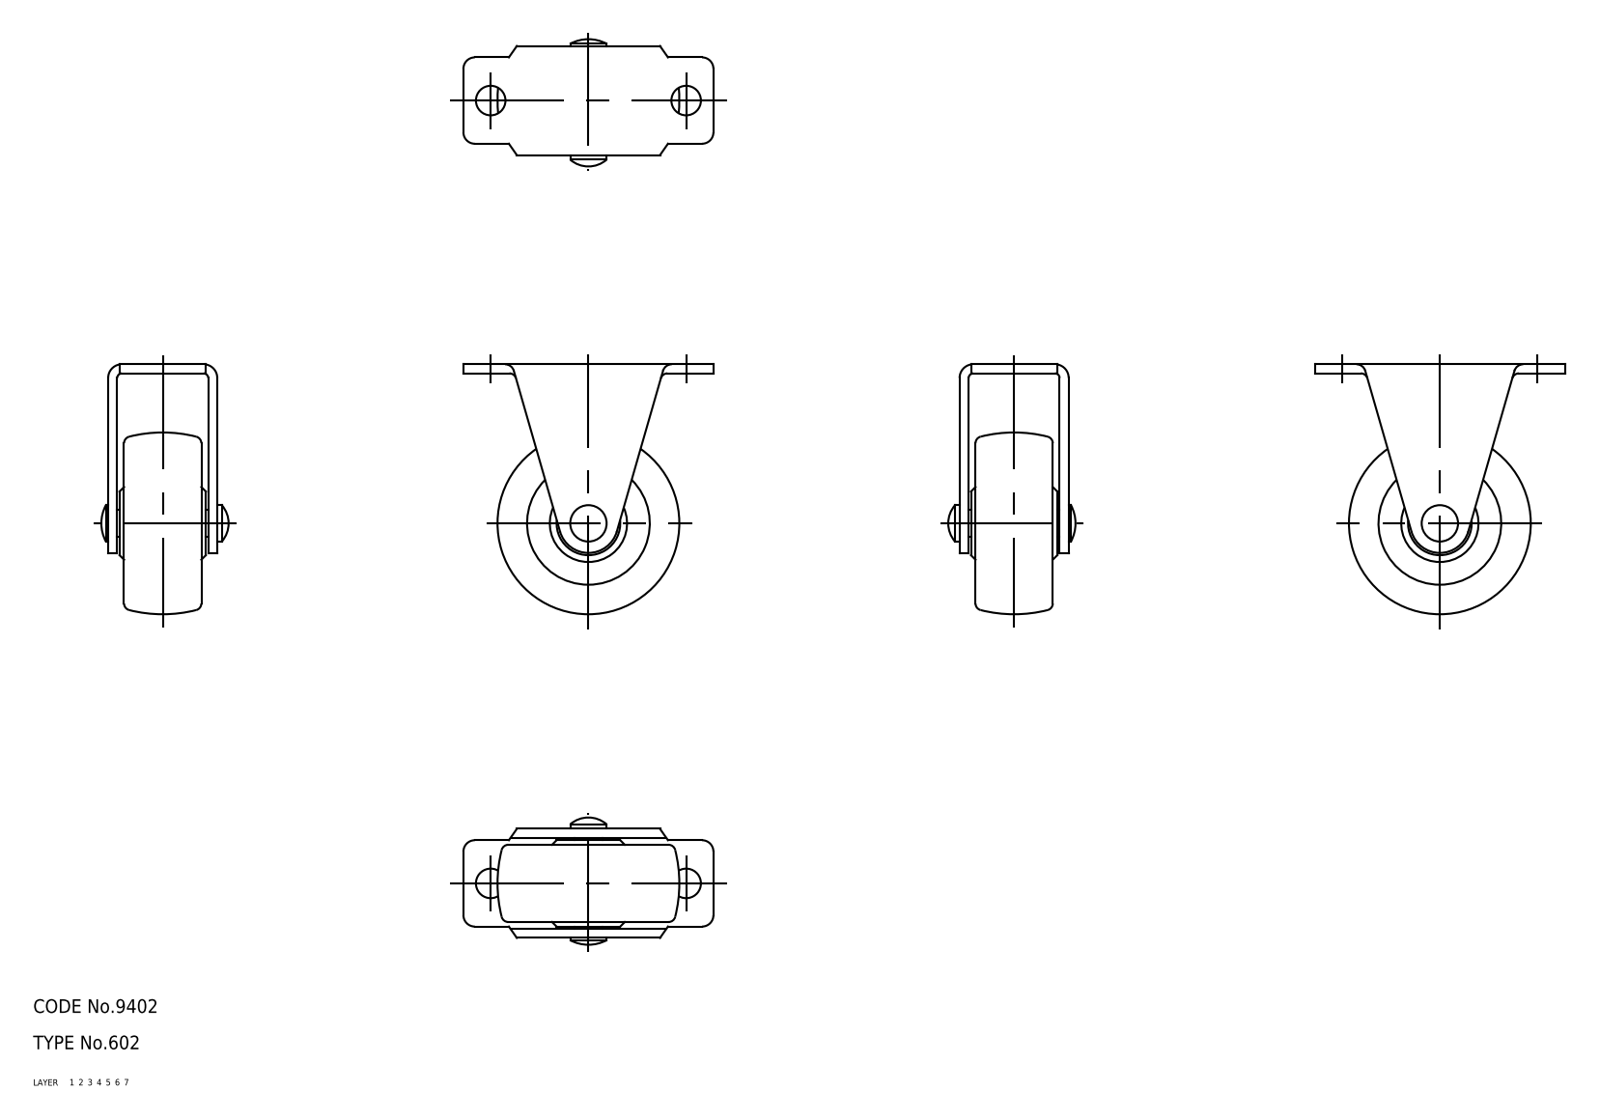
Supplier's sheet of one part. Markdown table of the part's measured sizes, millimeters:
| quantity | value |
| --- | --- |
| part name | wheel; axle; No_602_13552_36 |
| STEP written by | CADfix (AUTOMOTIVE_DESIGN) |
| units | millimeters |
| bodies | 3 solids, 90 faces (0 planar, 0 cylindrical, 90 other) |
| overall size | 55 × 55 × 28 |
| volume | 26 138 mm³ |
| surface area | 11 365 mm² |
